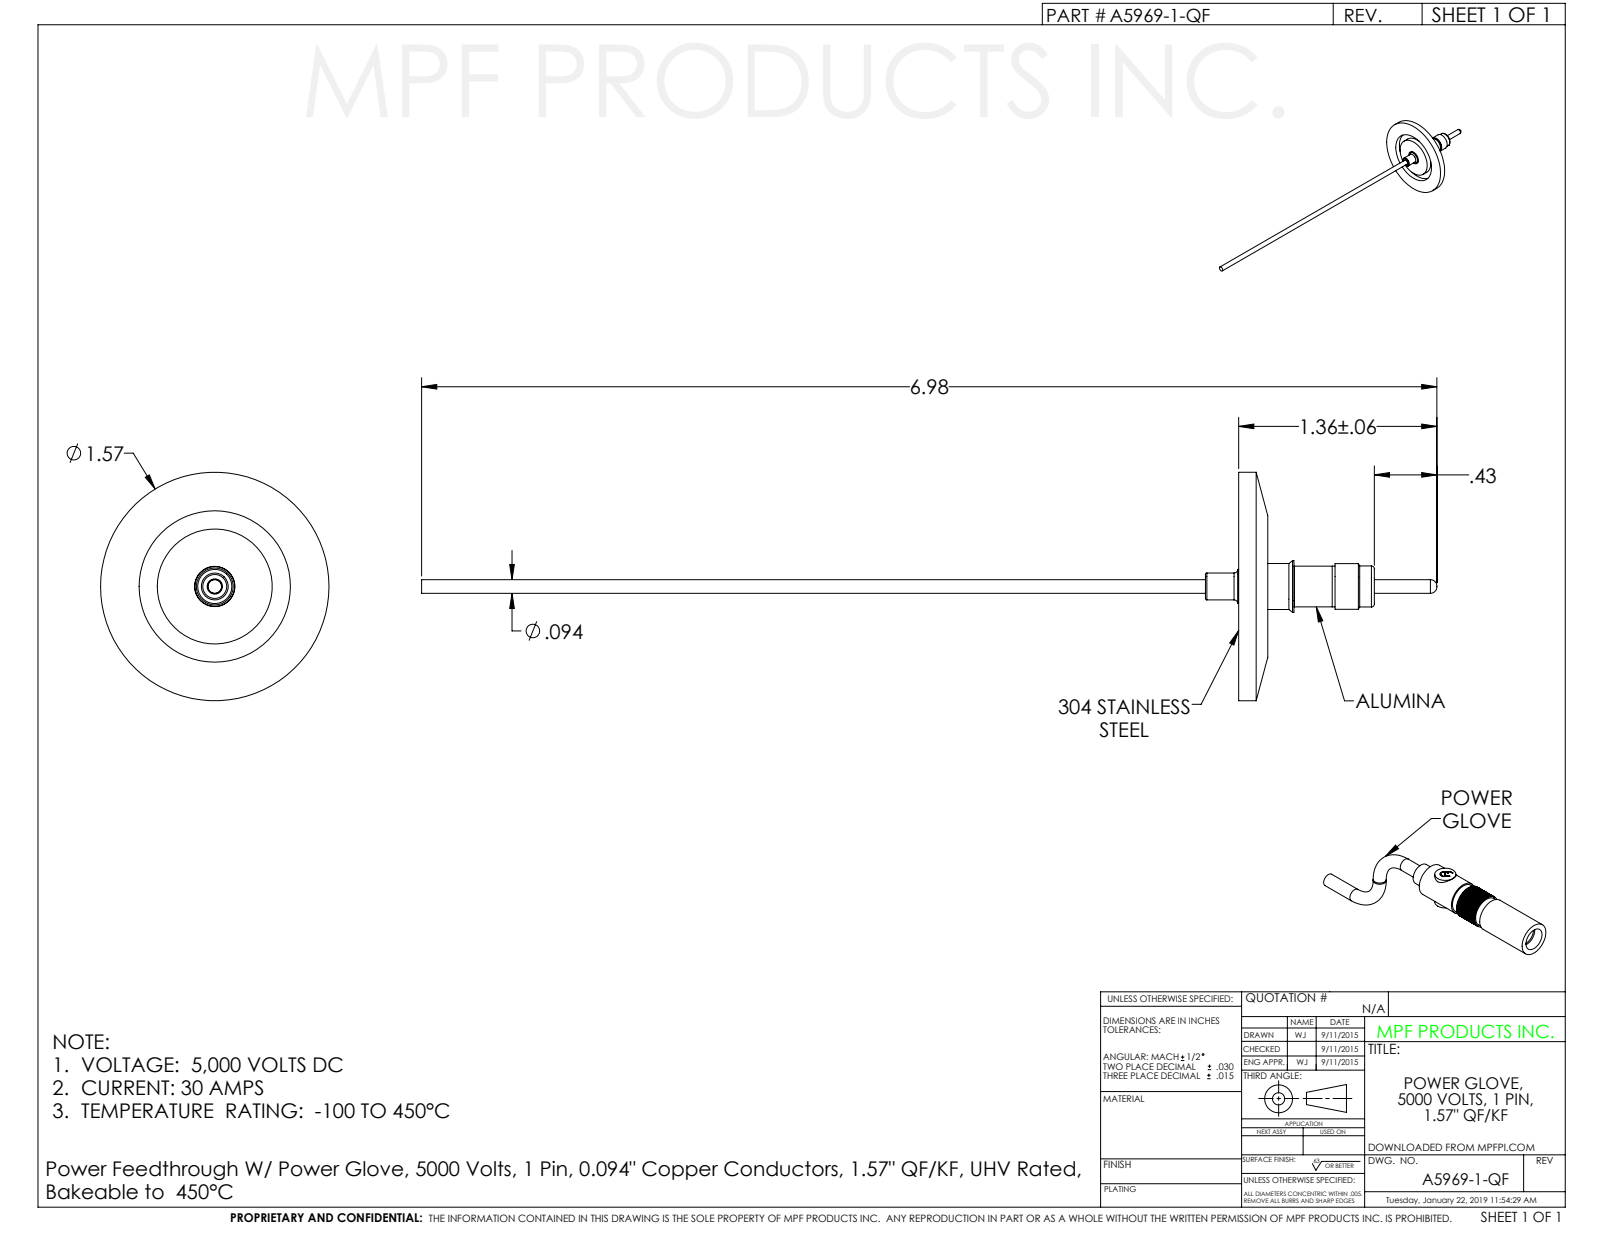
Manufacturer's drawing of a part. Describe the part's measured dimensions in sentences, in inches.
The part is named "A5969-1-QF". Its 3-D file was written by "SolidWorks 2012 (CONFIG_CONTROL_DESIGN)". It is 1 solid with 72 faces: 14 planar, 36 cylindrical and 22 other. Overall it measures 6.98 by 1.18 by 1.18 inches. Its volume is 0.253 cubic inches and its surface area 6.883 square inches. Round holes: 1 of diameter 0.105, 1 of diameter 0.254, 1 of diameter 0.259, 1 of diameter 0.274, 1 of diameter 0.277, 1 of diameter 0.82. Round bosses or shafts: 1 of diameter 1.18, 1 of diameter 0.62, 1 of diameter 0.312, 1 of diameter 0.311, 1 of diameter 0.287, 1 of diameter 0.285, 1 of diameter 0.28, 1 of diameter 0.243. The main face-to-face distances are 0.098, 0.2, 0.102, 0.935, 0.837, 0.735, 0.795, 0.697, 0.595, 0.14.
